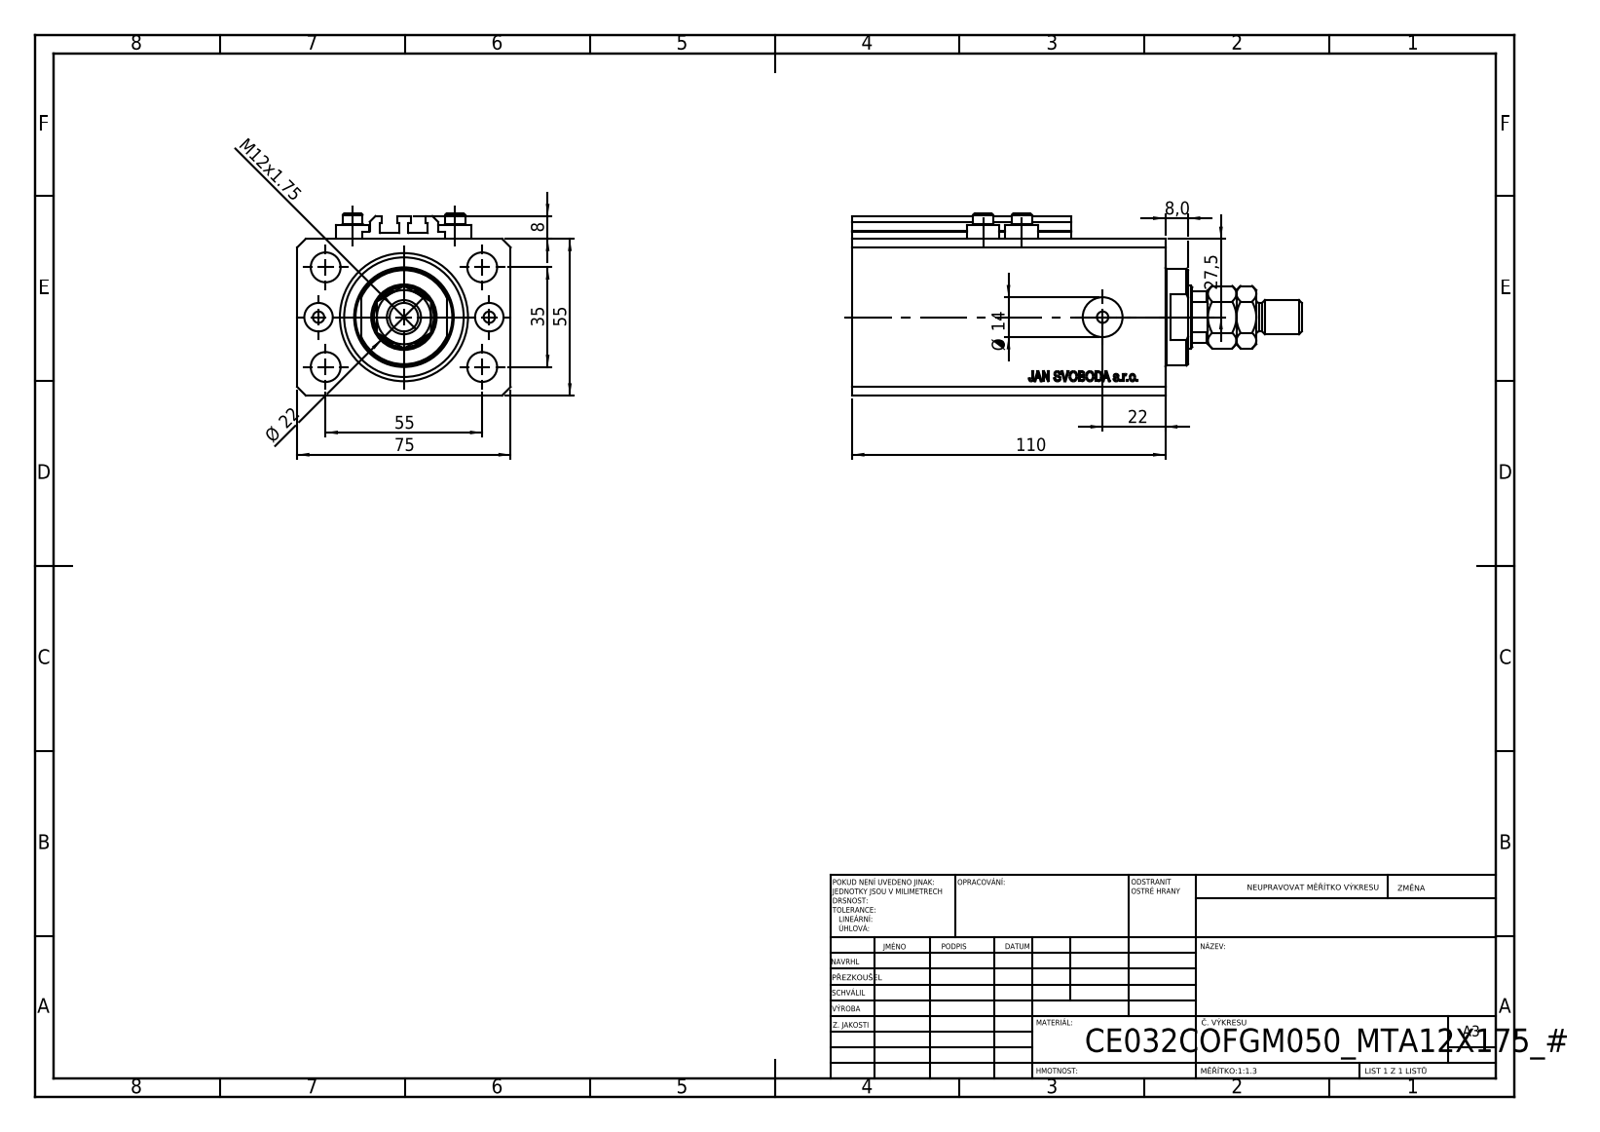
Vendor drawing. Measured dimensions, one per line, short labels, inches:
name: V250CE_VC_C; ALLEN BOLT V250CE; V250CE_C_VCP; V250CE_C_Body (+1 more)
written by: SolidWorks 2019 (CONFIG_CONTROL_DESIGN)
unit: in
bodies: 9 solids, 1083 faces (519 planar, 90 cylindrical, 474 other)
size: 6.22 × 2.953 × 2.52
volume: 25.38 in³; area: 144.8 in²
holes: 8× ⌀0.157, 5× ⌀0.413, 2× ⌀0.394, 2× ⌀0.551, 1× ⌀0.866, 1× ⌀1.26, 1× ⌀1.772
bosses: 4× ⌀0.457, 4× ⌀0.276, 1× ⌀1.339, 1× ⌀0.472, 1× ⌀0.394
rounds: 10× R0.008, 1× R0.413
face distances: 2.165, 2.953, 0.591, 4.331, 3.74, 0.39, 3.35, 3.941, 0.098, 0.118
hole spacings: 0.696, 1.283, 2.366, 0.535, 1.181, 1.378, 1.417, 1.515
